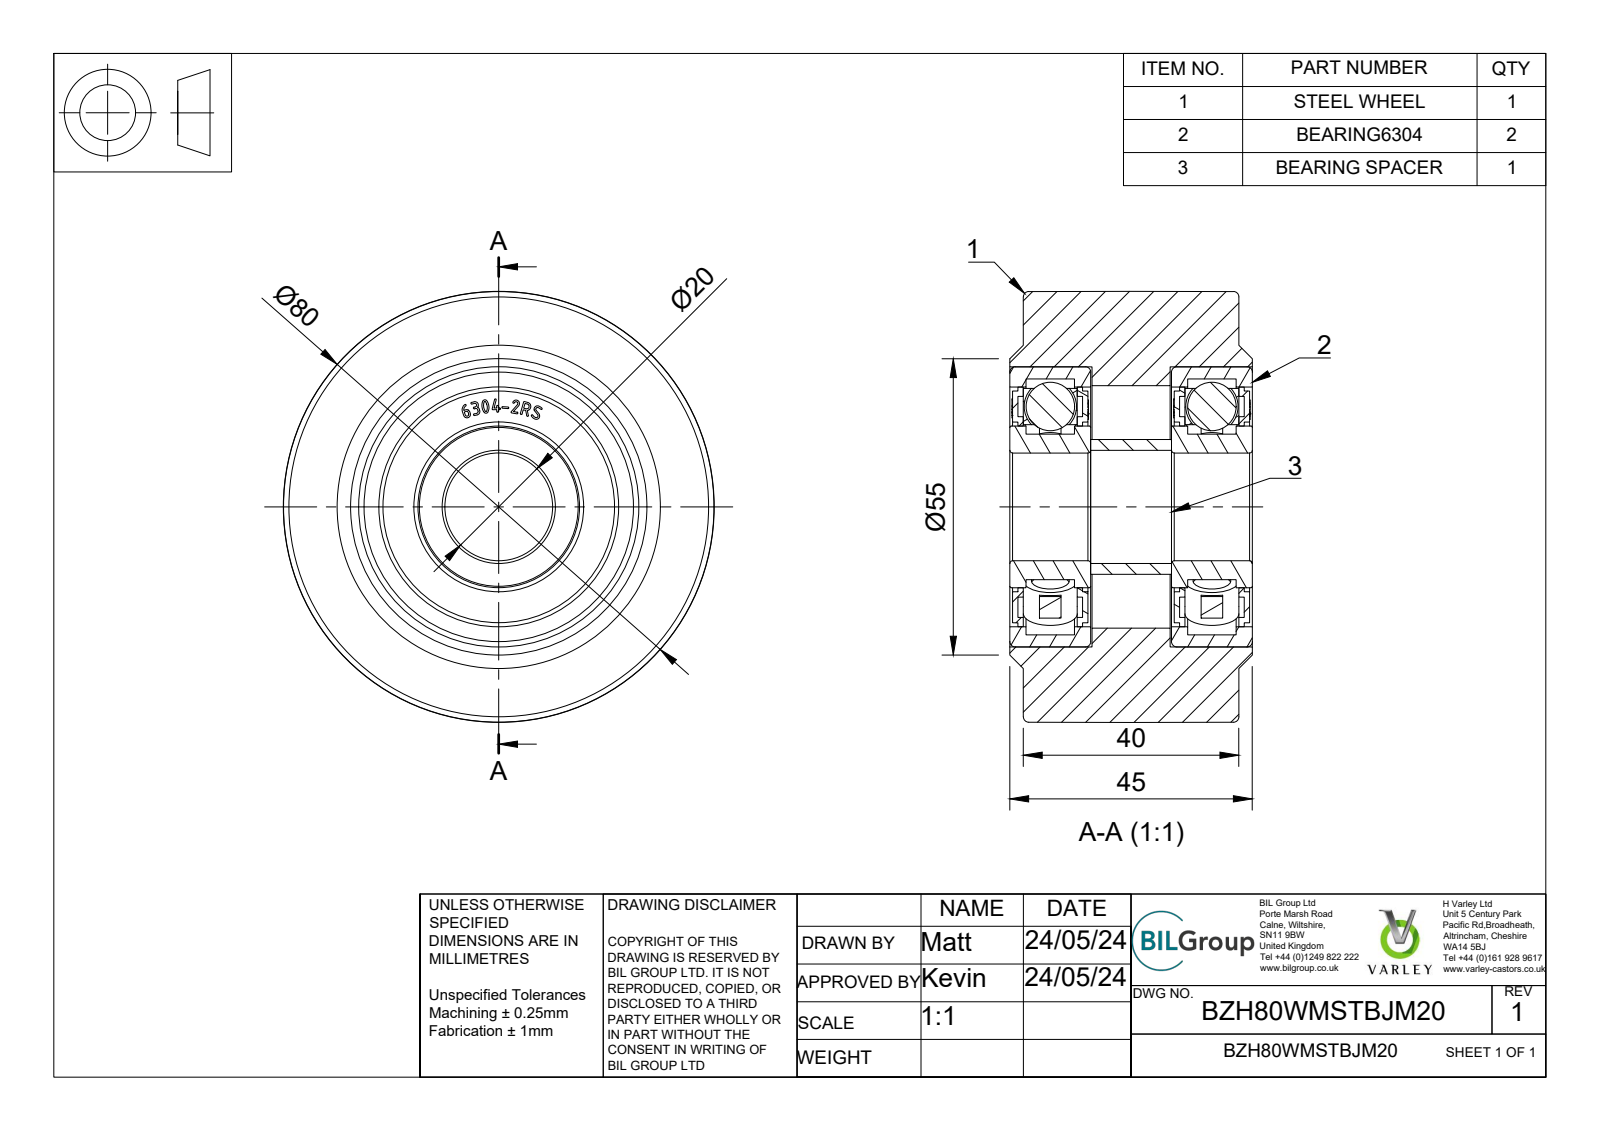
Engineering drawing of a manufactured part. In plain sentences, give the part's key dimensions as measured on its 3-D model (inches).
The part is named "BZH80WMSTBJM20 v3; wheel; BEARING6304 v1; BEARING6304 (+7 more)". Its 3-D file was written by "Autodesk Translation Framework v13.14.0.145 (AUTOMOTIVE_DESIGN)". It is 26 solids with 926 faces: 410 planar, 211 cylindrical and 305 other. Overall it measures 3.15 by 3.15 by 1.772 inches. Its volume is 9.989 cubic inches and its surface area 103.7 square inches. Round holes: 1 of diameter 0.787, 1 of diameter 0.827, 1 of diameter 1.181, 1 of diameter 1.24, 1 of diameter 1.614, 1 of diameter 1.752, 1 of diameter 1.772, 1 of diameter 1.87, 1 of diameter 2.047. Round bosses or shafts: 14 of diameter 0.394, 1 of diameter 1.693, 1 of diameter 1.319, 1 of diameter 1.063, 1 of diameter 0.984. Partial cylindrical surfaces (rounded edges, fillets, slot ends): 6 of radius 0.006, 4 of radius 0.013, 2 of radius 0.006, 2 of radius 0.006, 2 of radius 0.006, 2 of radius 0.006, 2 of radius 0.013, 2 of radius 0.017. The main face-to-face distances are 1.181, 0.039, 0.472, 0.098, 0.02, 0.571, 0.059, 0.591, 0.492, 0.531.
